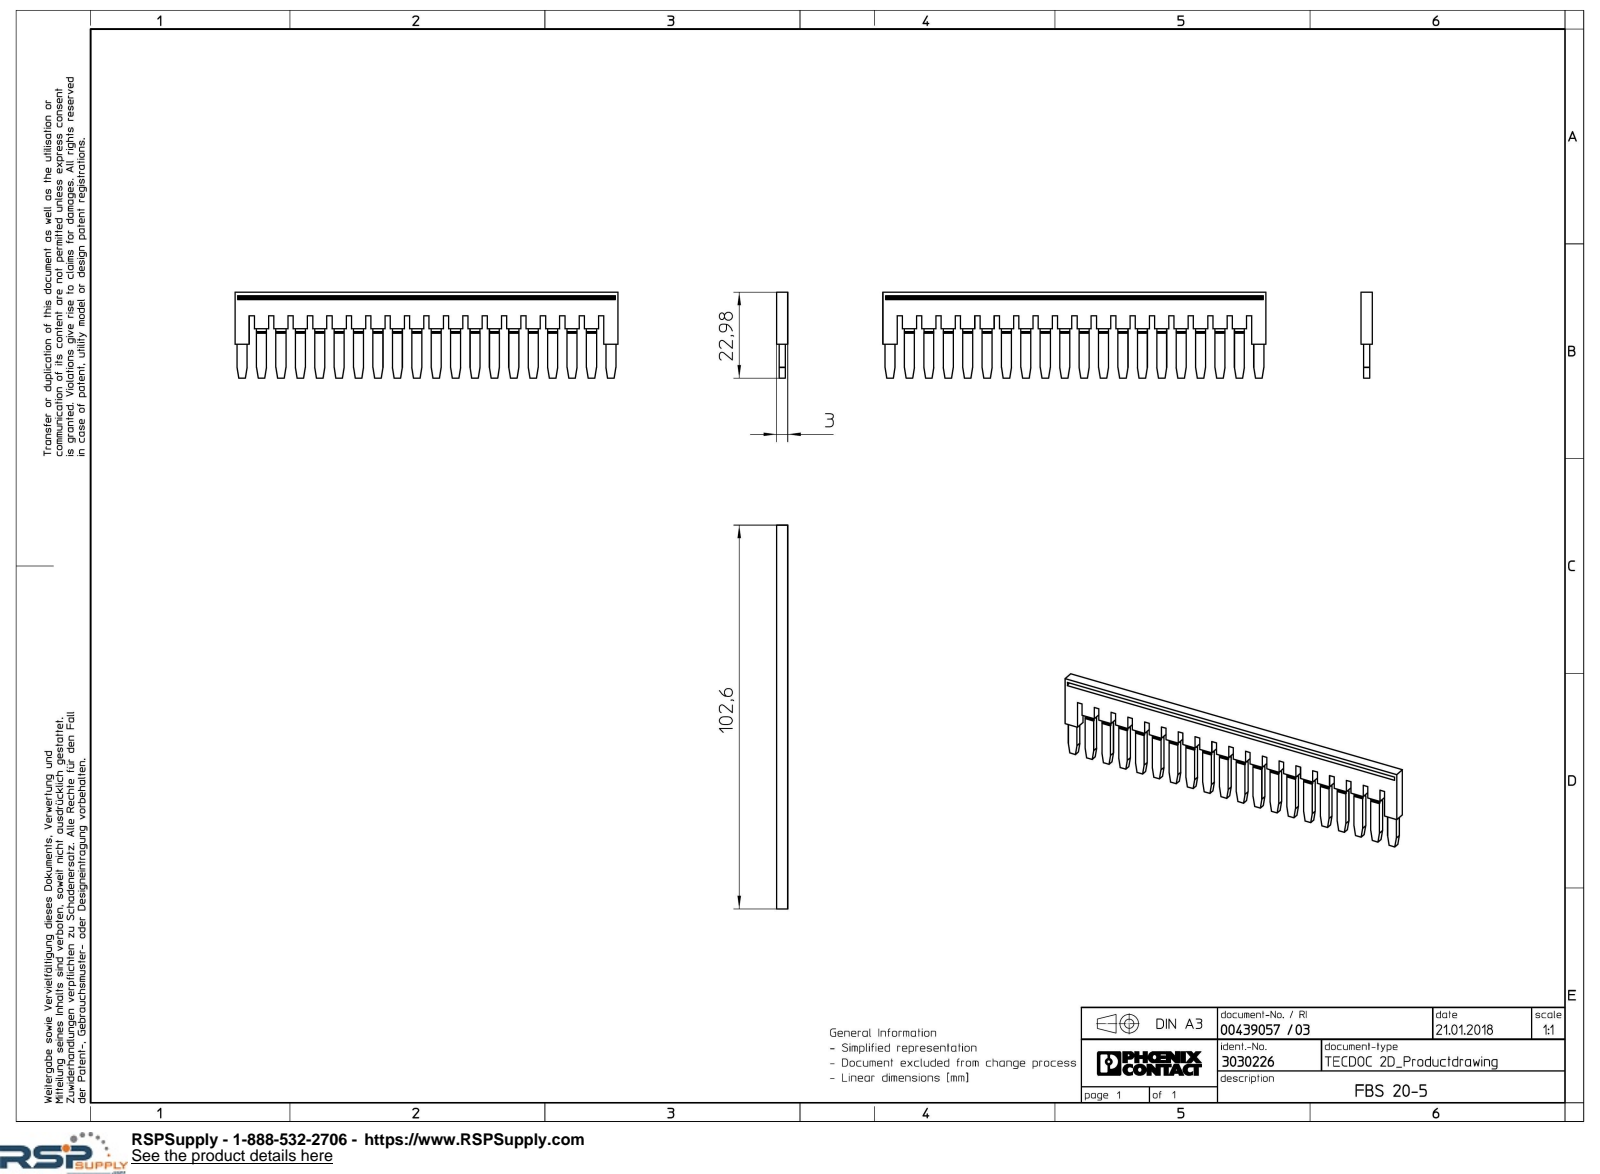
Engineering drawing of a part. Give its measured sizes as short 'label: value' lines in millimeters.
name: FBS_20_5-select
written by: Creo Elements/Direct Modeling 20.1A 29-Sep-2018 (C) Parametric Technology GmbH (AUTOMOTIVE_DESIGN)
unit: mm
bodies: 1 solid, 340 faces (340 planar, 0 cylindrical, 0 other)
size: 102.6 × 22.98 × 3
volume: 3 740 mm³; area: 5 436 mm²
face distances: 0.7, 2.3, 3, 1.6, 10.4, 5.2, 15.6, 20.8, 26, 20.53
